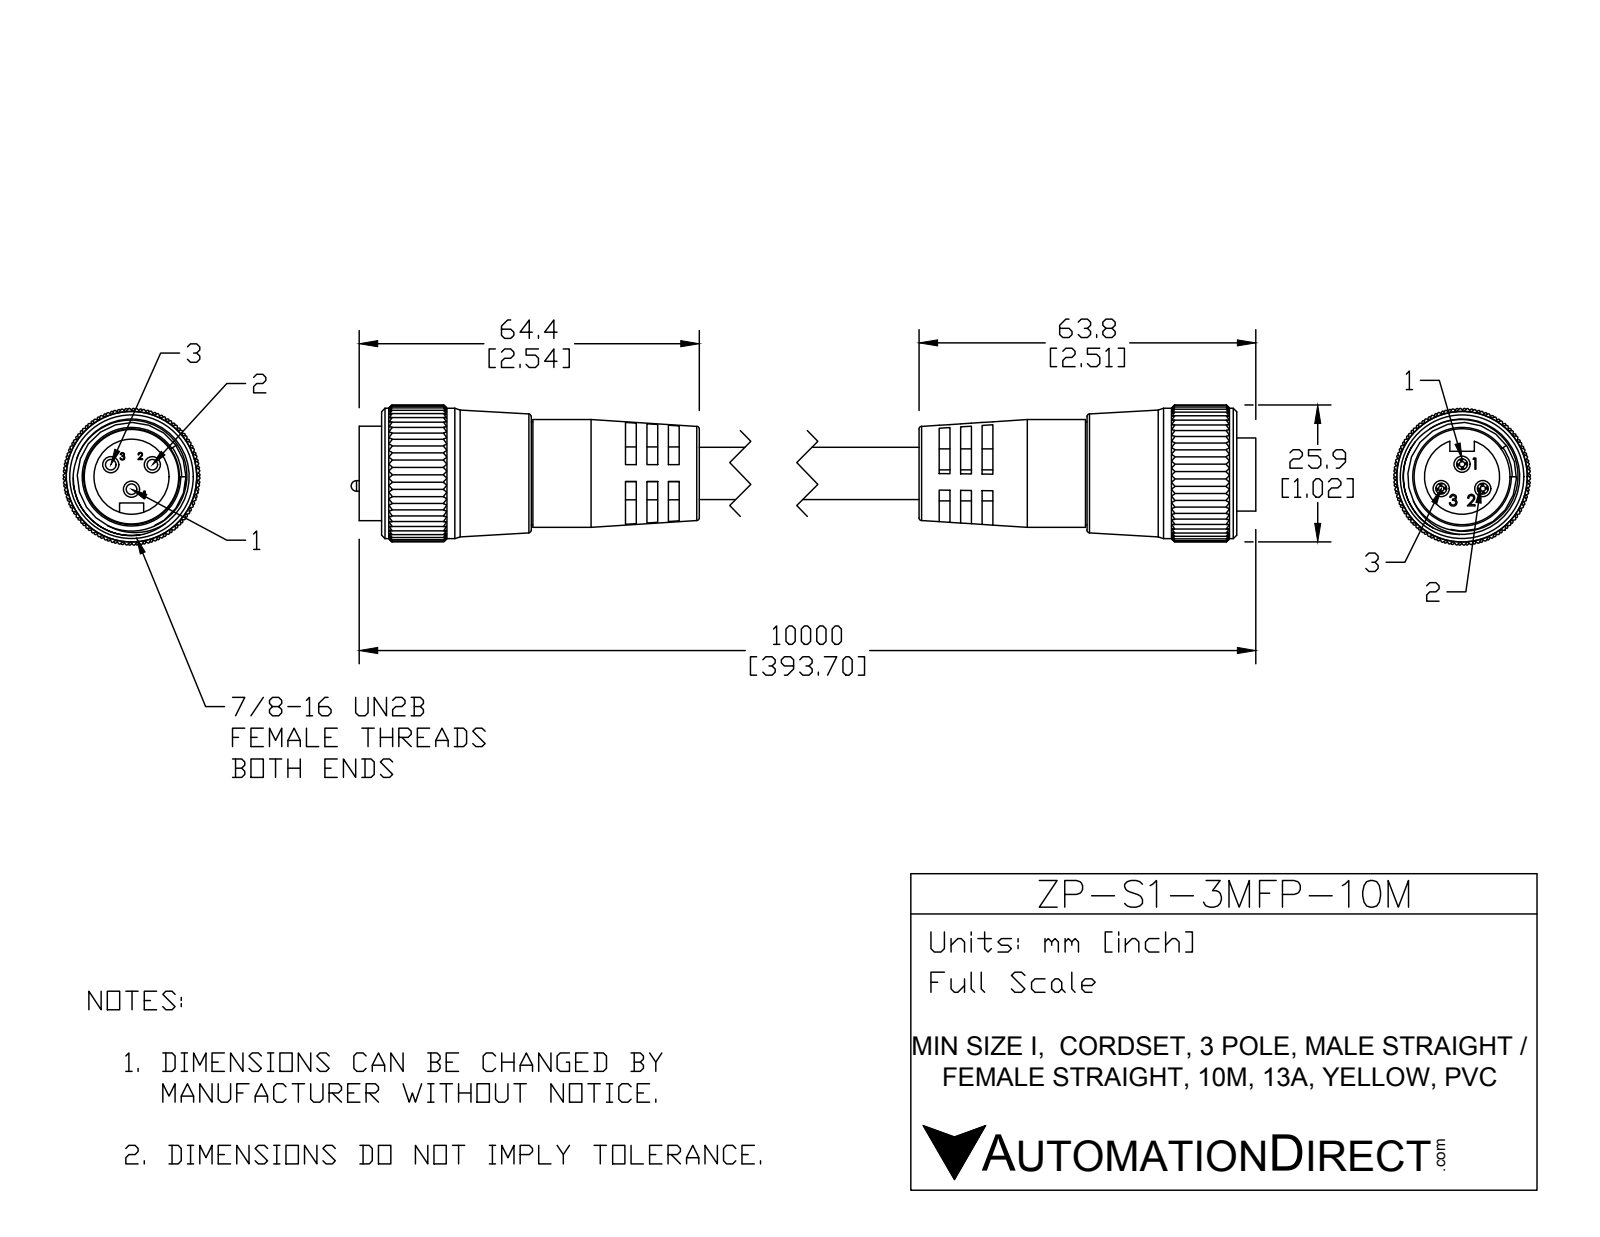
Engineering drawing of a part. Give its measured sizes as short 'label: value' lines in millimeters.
name: ZP-S1-3MFP-10M
written by: SolidWorks 2015 (AUTOMOTIVE_DESIGN)
unit: mm
bodies: 7 solids, 1099 faces (389 planar, 618 cylindrical, 92 other)
size: 229.66 × 25.84 × 25.83
volume: 50 808 mm³; area: 23 333 mm²
holes: 3× ⌀3.05, 1× ⌀19.96, 1× ⌀20.45, 1× ⌀21
bosses: 3× ⌀3.05, 3× ⌀2, 1× ⌀24.68, 1× ⌀20.4, 1× ⌀19.5, 1× ⌀17.88, 1× ⌀14.22, 1× ⌀9.91
rounds: 165× R0.25, 1× R2.29, 1× R5.25, 1× R12.93
face distances: 2, 4.02, 117.68, 113.65, 4.03, 125.74, 59.84, 4.04, 121.7, 121.72
hole spacings: 6.07, 2.36, 4.53, 4.54, 7.87
